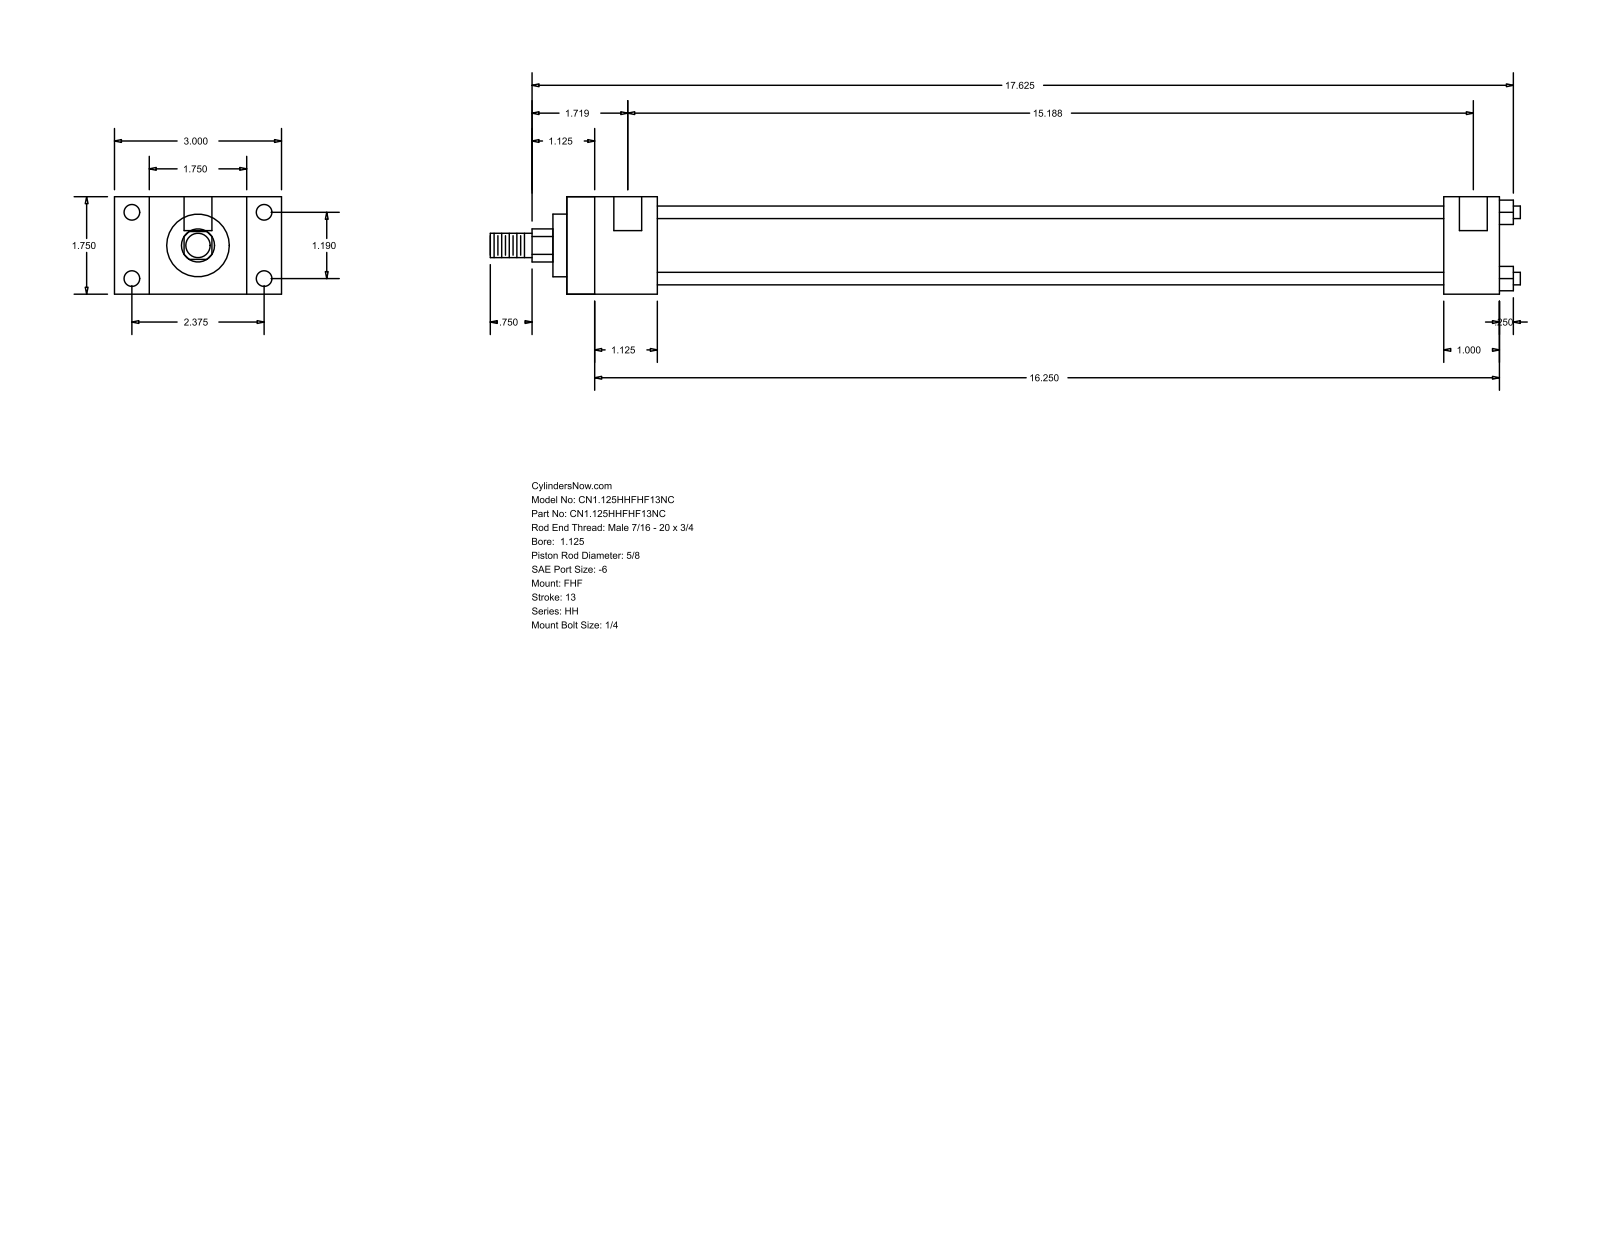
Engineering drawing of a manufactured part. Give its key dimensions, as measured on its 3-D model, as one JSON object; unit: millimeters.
{"part_name": "HH_FHF__0112_0.625", "step_written_by": "GSSL Pune (CONFIG_CONTROL_DESIGN)", "units": "millimeters", "bodies": {"solids": 0, "faces": 88, "planar": 60, "cylindrical": 28, "other": 0}, "overall_size": [469.9, 76.2, 44.45], "round_holes": [[5.56, 4], [7.14, 4], [12.7, 2]], "round_bosses_or_shafts": [[5.71, 4], [34.92, 1], [28.57, 1], [15.88, 1], [11.11, 1]], "partial_cylinders_radius": [[7.54, 1]], "face_to_face_distances": [44.46, 15.87, 60.33, 41.27, 76.2, 425.44, 384.17, 400.05, 358.78, 25.39], "hole_center_spacings": [30.22, 60.32, 67.47, 382.59, 3.17, 385.76]}
